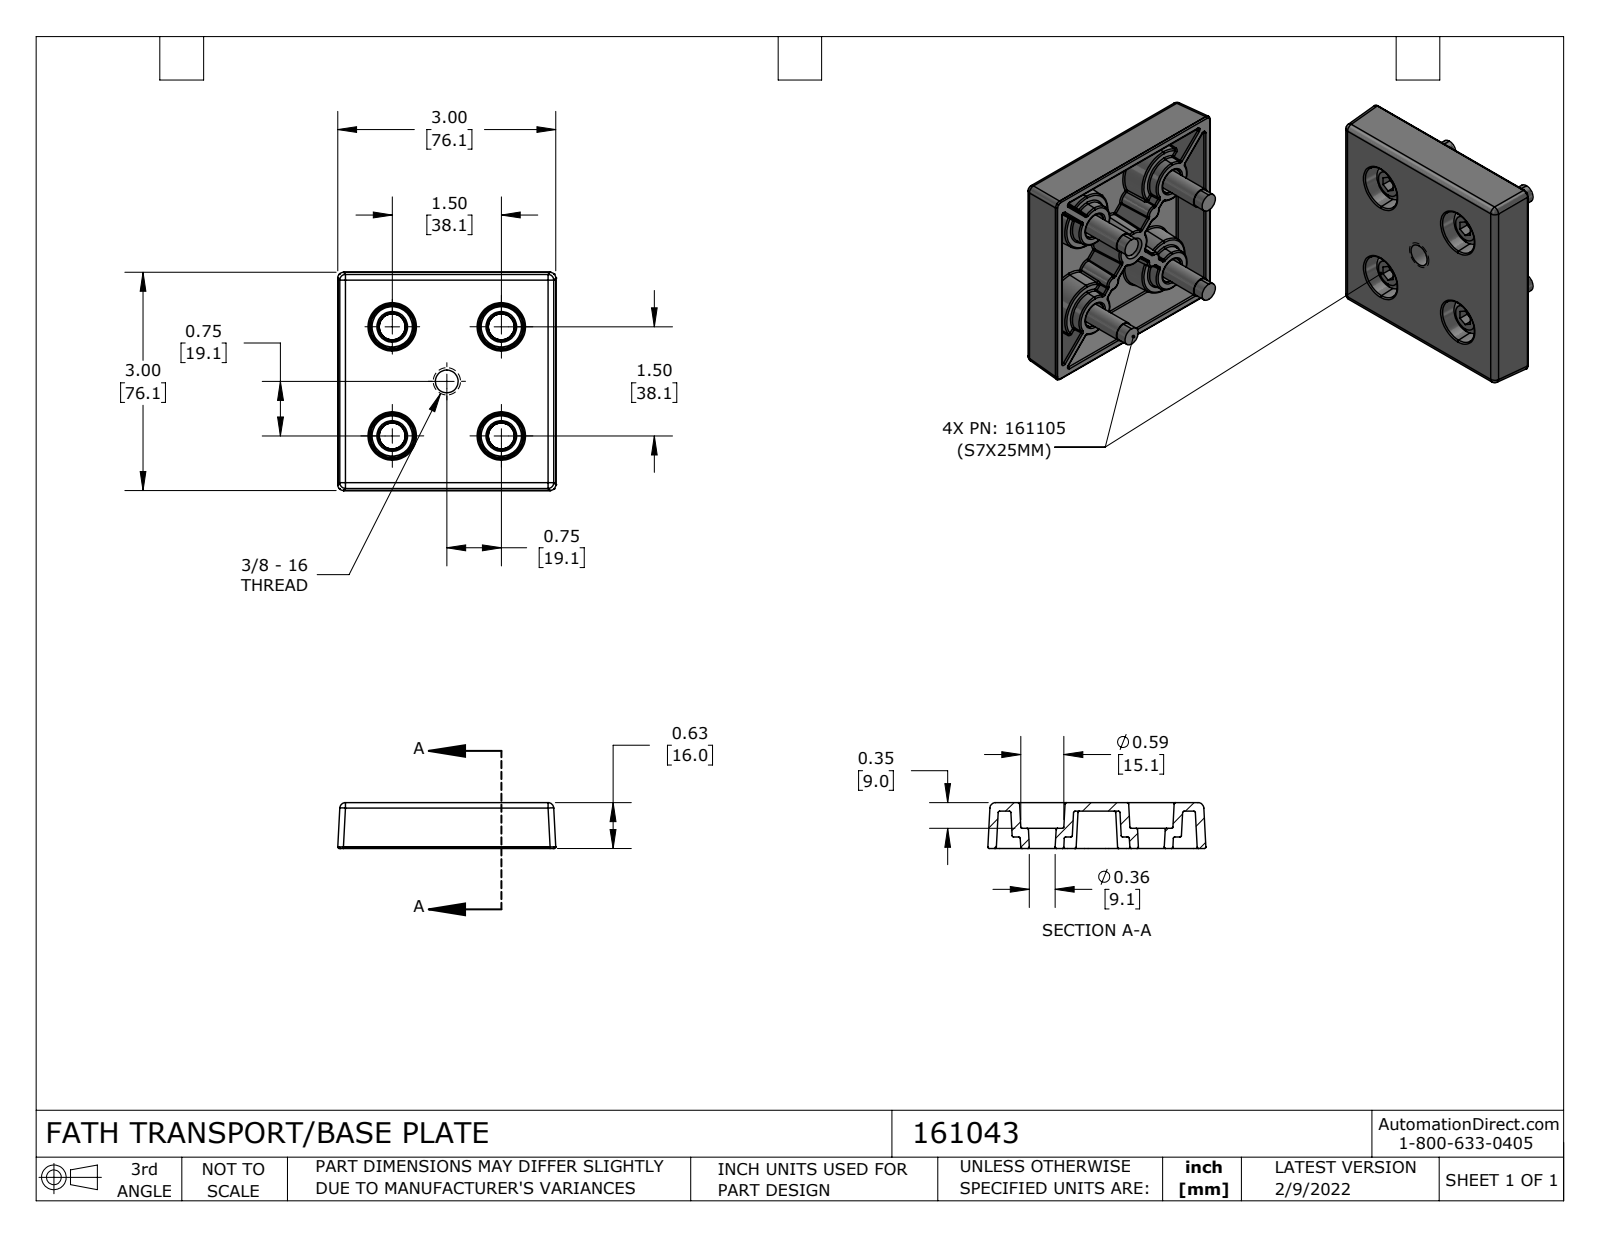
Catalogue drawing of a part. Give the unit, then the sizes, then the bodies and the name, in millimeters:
Units: millimetres
Overall size (bounding box): 76.15 × 76.15 × 16
Round holes (diameter × count): ⌀7.94 ×1
Partial cylindrical surfaces — rounded edges, fillets, slot ends (radius × count): R0.5 ×48, R2 ×8
Main face-to-face distances: 3, 13, 16, 9, 4, 12, 7, 6
Volume: 40 849 mm³ · Surface area: 25 765 mm²
Bodies: 1 solid, 548 faces (50 planar, 91 cylindrical, 407 other)
Part name (STEP PRODUCT): 161043
STEP written by: SolidWorks 2021 (CONFIG_CONTROL_DESIGN)
